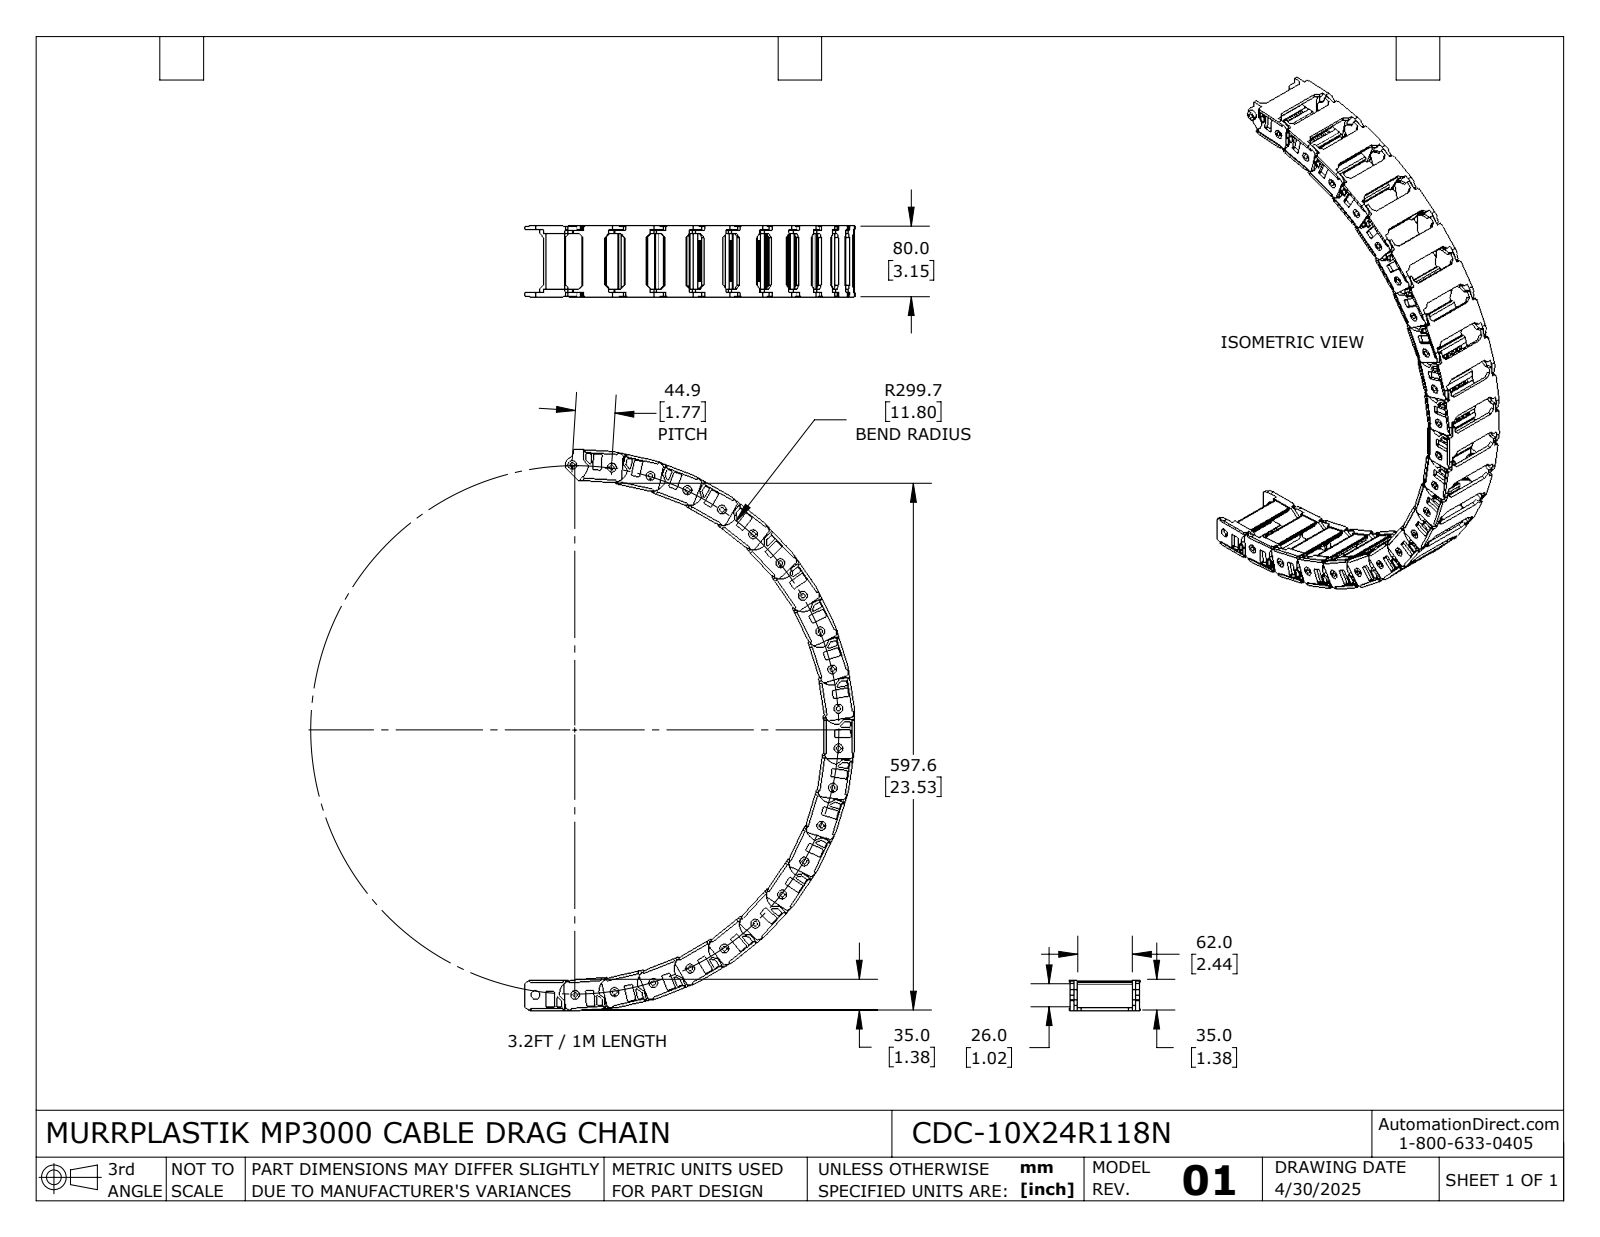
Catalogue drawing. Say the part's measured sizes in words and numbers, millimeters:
The part is named "CDC-10X24R118N". Its 3-D file was written by "SolidWorks 2024 (AUTOMOTIVE_DESIGN)". It is 22 solids with 4400 faces: 3300 planar, 1100 cylindrical and 0 other. Overall it measures 635.4 by 373.99 by 80 millimeters. Its volume is 679 888 cubic millimeters and its surface area 413 031 square millimeters. Round holes: 22 of diameter 5.1, 22 of diameter 10.1. Round bosses or shafts: 22 of diameter 10. Partial cylindrical surfaces (rounded edges, fillets, slot ends): 176 of radius 1, 88 of radius 0.5, 44 of radius 1.5, 44 of radius 2, 44 of radius 21, 22 of radius 2.8, 22 of radius 8, 22 of radius 18. The main face-to-face distances are 70, 8, 4, 3.7, 74.3, 4.3, 66.3, 3.5, 62, 0.8. The hole center spacings are 89.64, 177.26, 133.83, 44.95, 45, 44.94, 89.69, 133.88.
